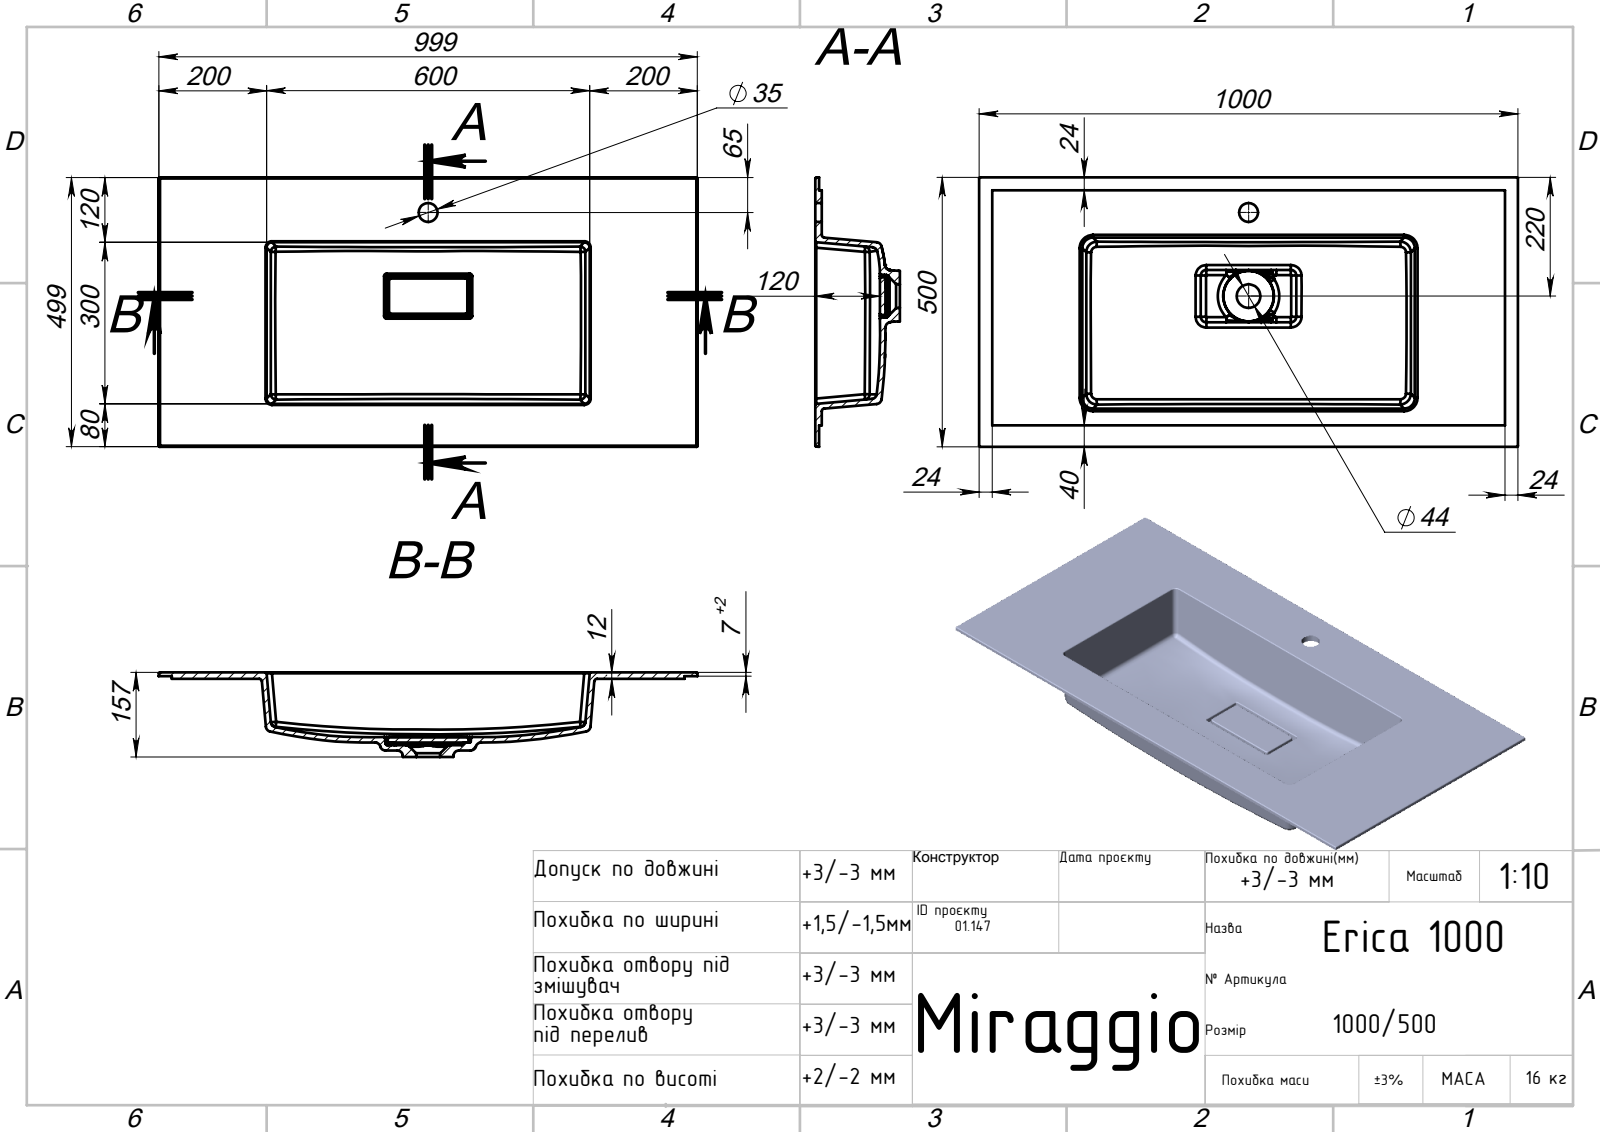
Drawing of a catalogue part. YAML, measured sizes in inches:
part_name: "Erica 1000"
step_written_by: "SolidWorks 2020 (AUTOMOTIVE_DESIGN)"
units: inches
bodies: {solids: 2, faces: 244, planar: 44, cylindrical: 69, other: 131}
overall_size: [39.37, 19.685, 6.181]
volume: 438.2
surface_area: 2162
round_holes:
  - {diameter: 1.378, count: 1}
partial_cylinders:
  - {radius: 0.079, count: 27}
  - {radius: 0.118, count: 19}
  - {radius: 0.236, count: 6}
  - {radius: 0.197, count: 4}
  - {radius: 0.394, count: 4}
  - {radius: 0.787, count: 4}
face_to_face_distances: [0.472, 0.394, 0.197, 0.276, 0.393, 4.843, 4.646, 5.118, 4.252, 4.449]
